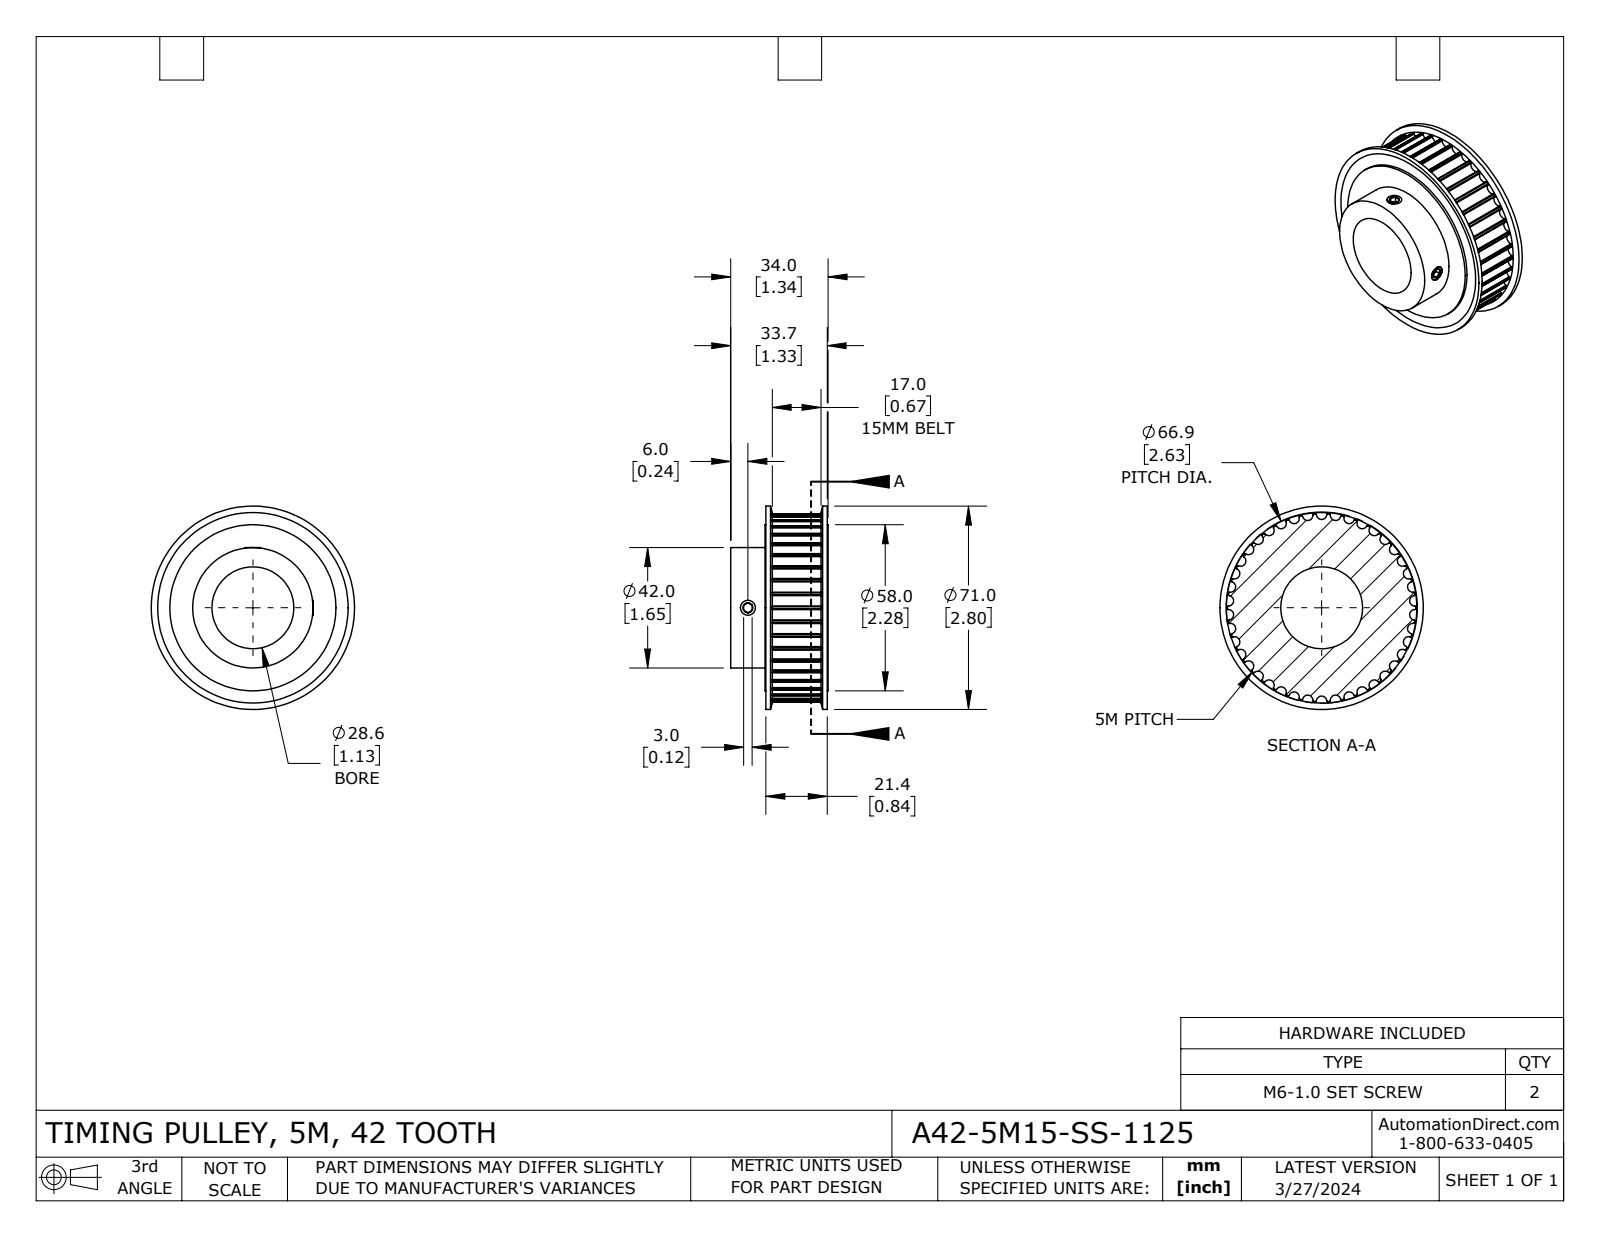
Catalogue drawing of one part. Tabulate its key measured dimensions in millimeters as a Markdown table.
| quantity | value |
| --- | --- |
| part name | A42-5M15-SS-1125 |
| STEP written by | SolidWorks 2021 (CONFIG_CONTROL_DESIGN) |
| units | millimeters |
| bodies | 5 solids, 292 faces (25 planar, 233 cylindrical, 34 other) |
| overall size | 71 × 71 × 34 |
| volume | 65 622 mm³ |
| surface area | 22 627 mm² |
| round holes (diameter × count) | 5 × 2, 28.58 × 1, 58 × 1 |
| round bosses / shafts (diameter × count) | 6 × 2, 71 × 1, 42 × 1 |
| partial cylindrical surfaces (radius × count) | 0.3 × 84, 1.82 × 42, 32.85 × 1 |
| main face-to-face distances | 2.5, 19.5, 0.9, 21.1, 1.6, 18.6, 17, 22, 20.2, 34 |
